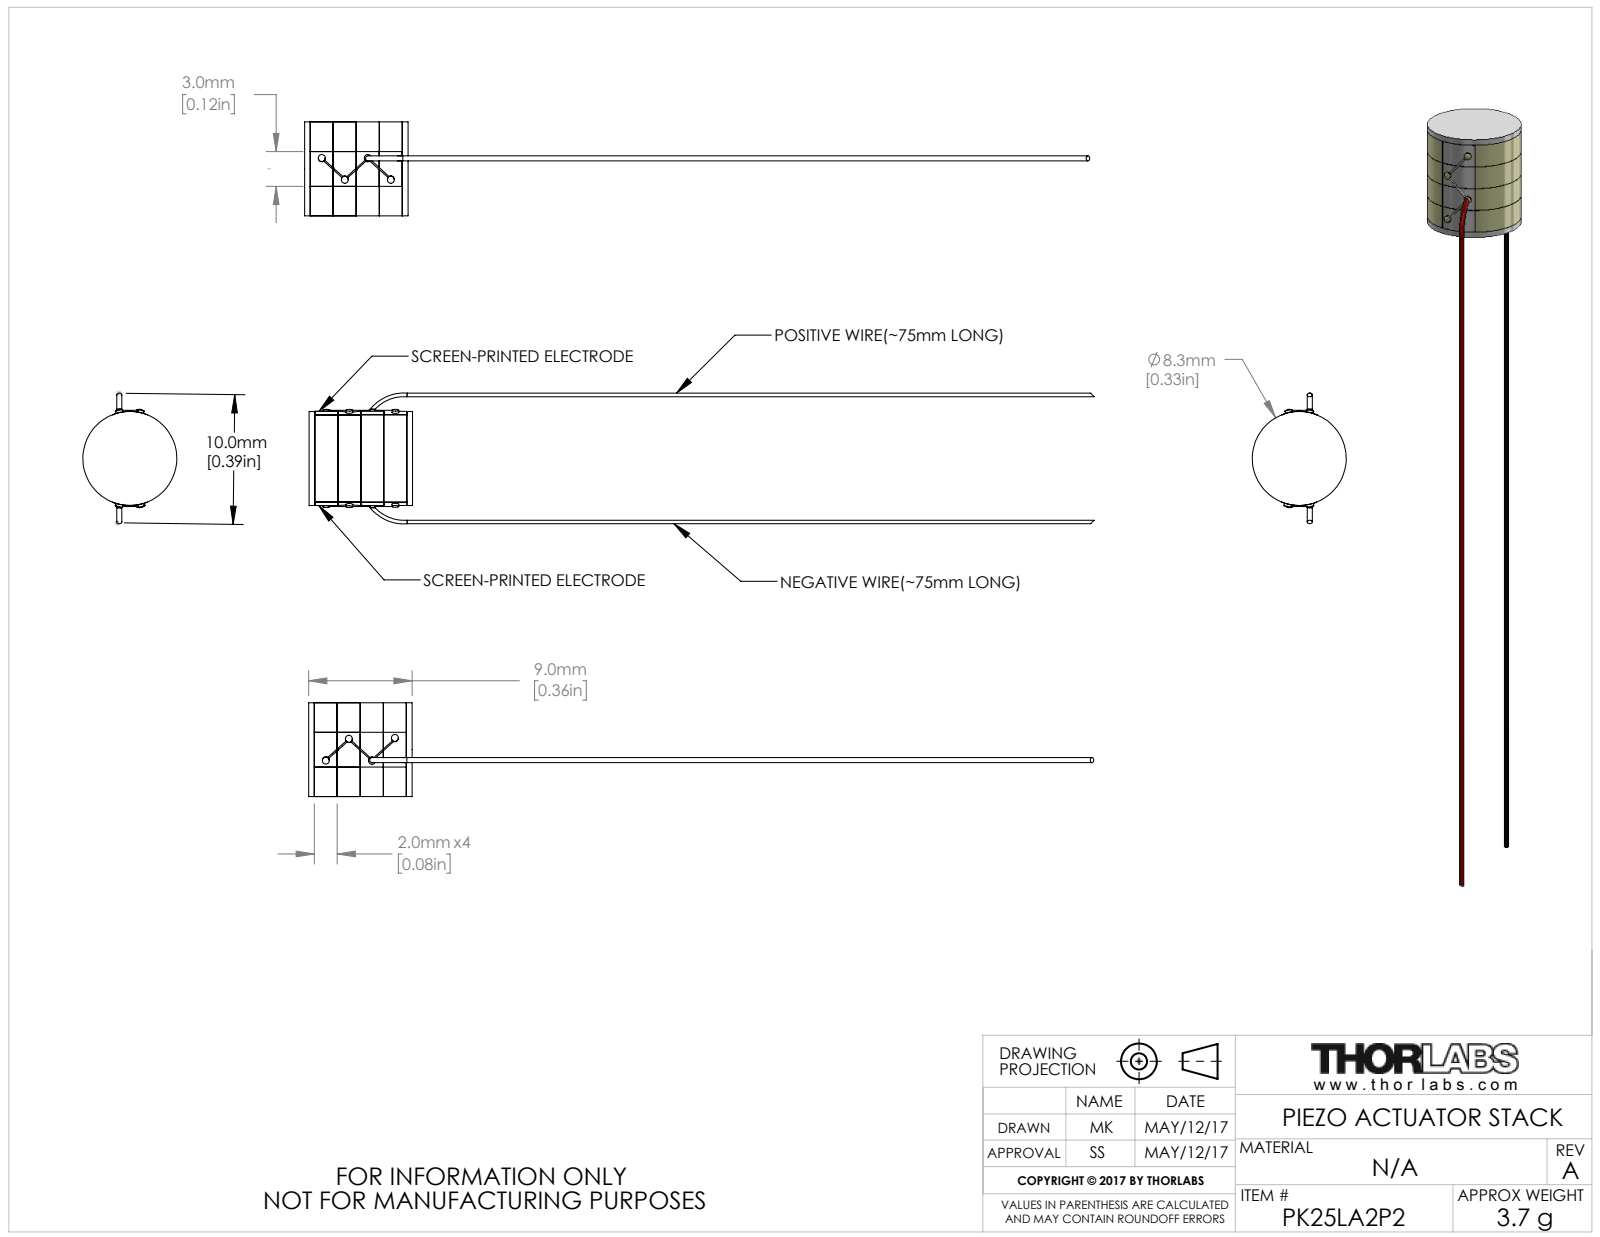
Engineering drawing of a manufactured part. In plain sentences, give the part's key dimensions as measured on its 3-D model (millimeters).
The part is named "CTN009558". Its 3-D file was written by "SolidWorks 2016 (AUTOMOTIVE_DESIGN)". It is 8 solids with 142 faces: 62 planar, 36 cylindrical and 44 other. Overall it measures 68.55 by 11.43 by 8.2 millimeters. Its volume is 702 cubic millimeters and its surface area 1 340 square millimeters. Round bosses or shafts: 1 of diameter 8.2. Partial cylindrical surfaces (rounded edges, fillets, slot ends): 1 of radius 4.11. The main face-to-face distances are 2.01, 2, 4.02, 4.01, 6.02, 6.03, 2.02, 8.03, 0.5, 2.5.
